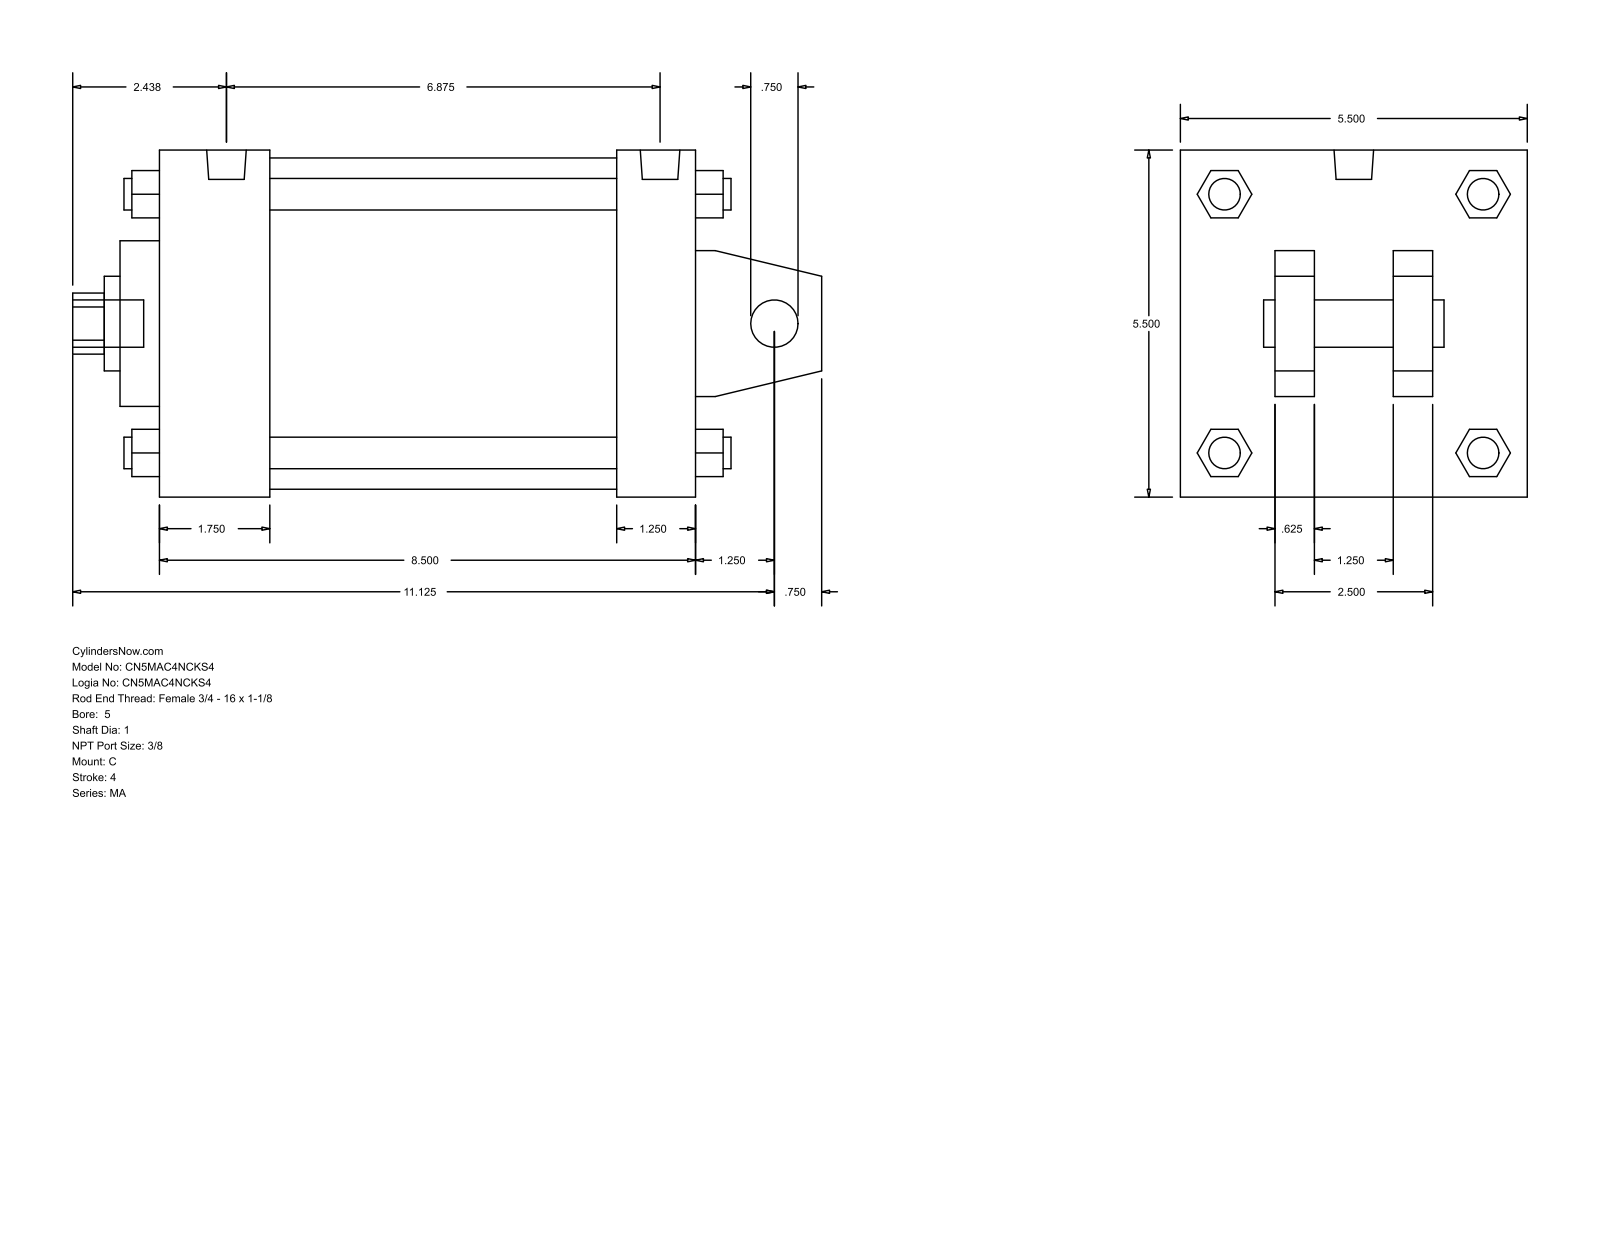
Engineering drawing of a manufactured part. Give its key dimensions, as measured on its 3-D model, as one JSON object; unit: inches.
{"part_name": "MA_C__0500_1", "step_written_by": "GSSL Pune (CONFIG_CONTROL_DESIGN)", "units": "inches", "bodies": {"solids": 0, "faces": 141, "planar": 109, "cylindrical": 32, "other": 0}, "overall_size": [11.875, 5.5, 5.5], "round_holes": [[0.75, 1], [1, 1], [1.5, 1], [2.625, 1], [5.25, 1]], "round_bosses_or_shafts": [[0.5, 4], [0.437, 4], [0.627, 2], [0.75, 1]], "partial_cylinders_radius": [[0.484, 1]], "face_to_face_distances": [5.5, 8.5, 0.625, 7.25, 1.25, 1.75, 5.5, 6.75, 1.5, 4]}
